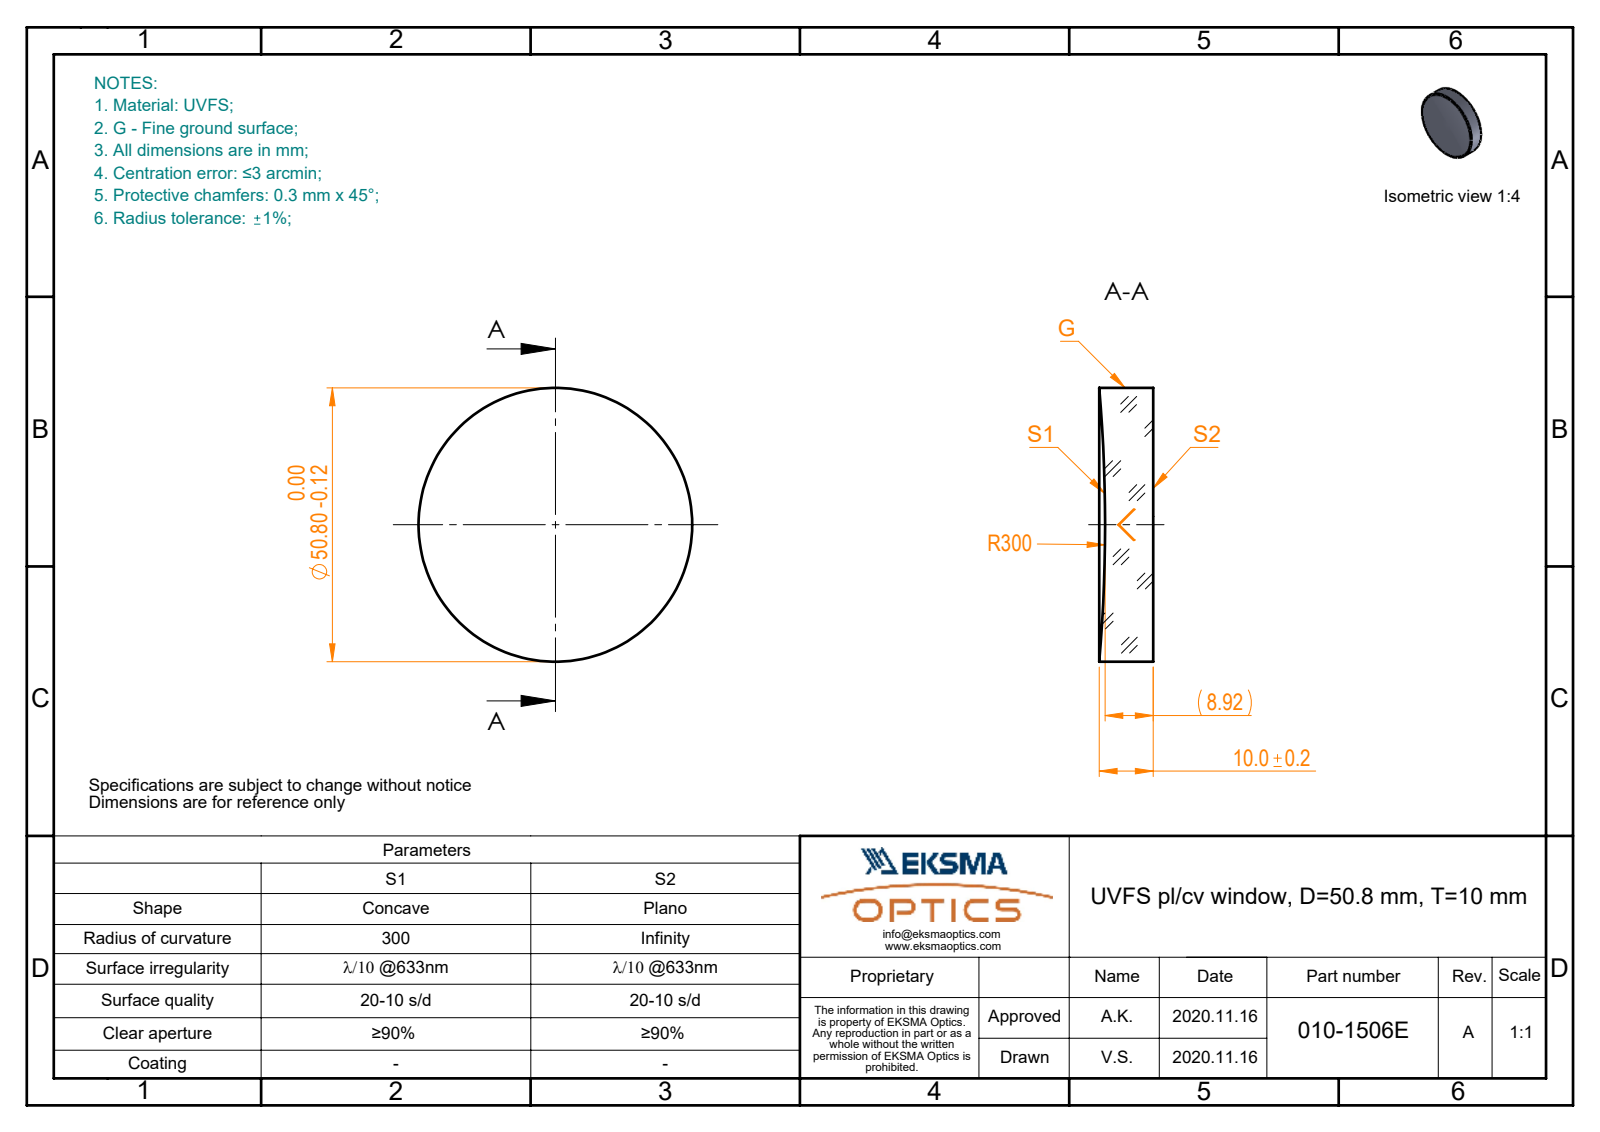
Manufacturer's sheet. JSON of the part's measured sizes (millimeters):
{"part_name": "010-1506E_UVFS_PCV_window", "step_written_by": "SolidWorks 2019 (CONFIG_CONTROL_DESIGN)", "units": "millimeters", "bodies": {"solids": 1, "faces": 5, "planar": 1, "cylindrical": 2, "other": 2}, "overall_size": [50.8, 50.8, 10], "volume_mm3": 19176, "surface_area_mm2": 5653, "round_bosses_or_shafts": [[50.8, 1]]}
